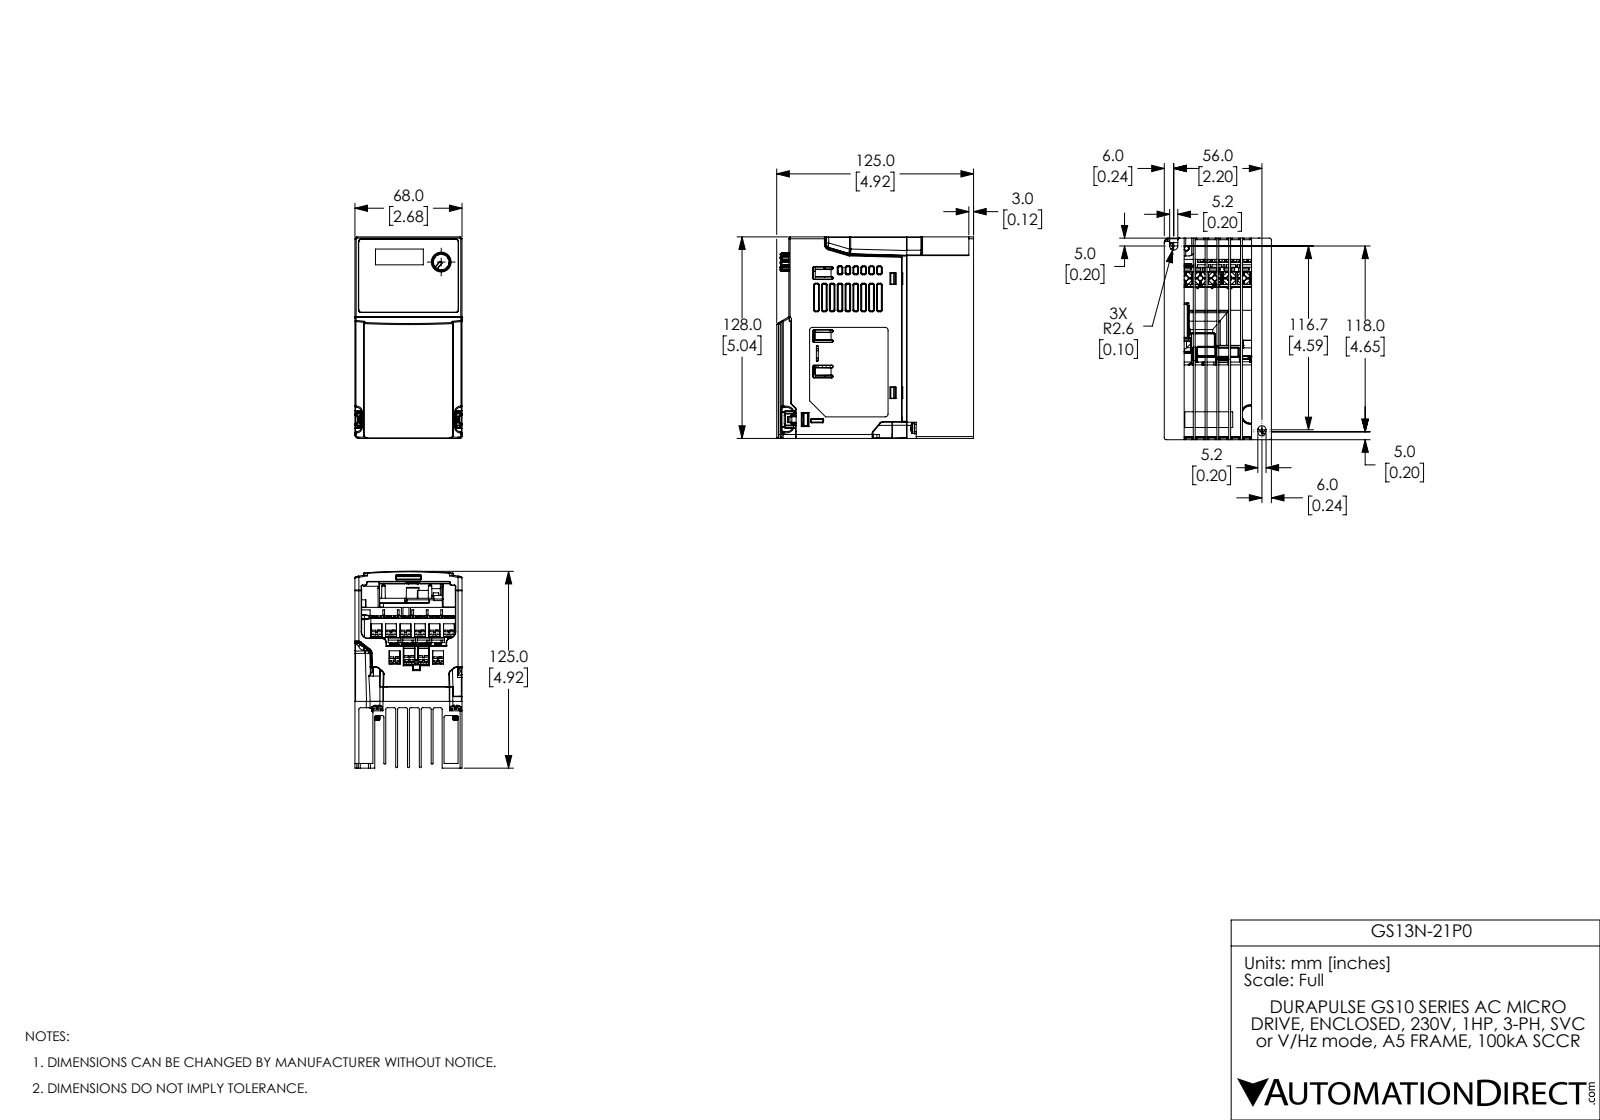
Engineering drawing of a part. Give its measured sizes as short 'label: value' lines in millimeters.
name: DELTA_IA_MDS_VFD-ME300-A3_D-3D_20190924 from Step R1 red1 r3cC for A5bB
written by: SolidWorks 2017 (AUTOMOTIVE_DESIGN)
unit: mm
bodies: 33 solids, 5891 faces (3121 planar, 1268 cylindrical, 1502 other)
size: 128 × 125 × 68
volume: 140 373 mm³; area: 191 680 mm²
holes: 10× ⌀3.15, 2× ⌀3.3, 2× ⌀4.8, 1× ⌀3.9, 1× ⌀10.9, 1× ⌀12.6
bosses: 12× ⌀6.8, 12× ⌀2.76, 10× ⌀3.5, 2× ⌀4.2, 2× ⌀3.4
rounds: 148× R0.5, 141× R0.3, 84× R0.4, 68× R0.2, 32× R1, 30× R0.8, 27× R3, 21× R2
face distances: 7.5, 1.2, 15, 29.5, 6.3, 14.5, 22, 8.7, 37, 7
hole spacings: 9.2, 18.4, 14.34, 15.74, 18.23, 27.6, 20.85, 21.43
